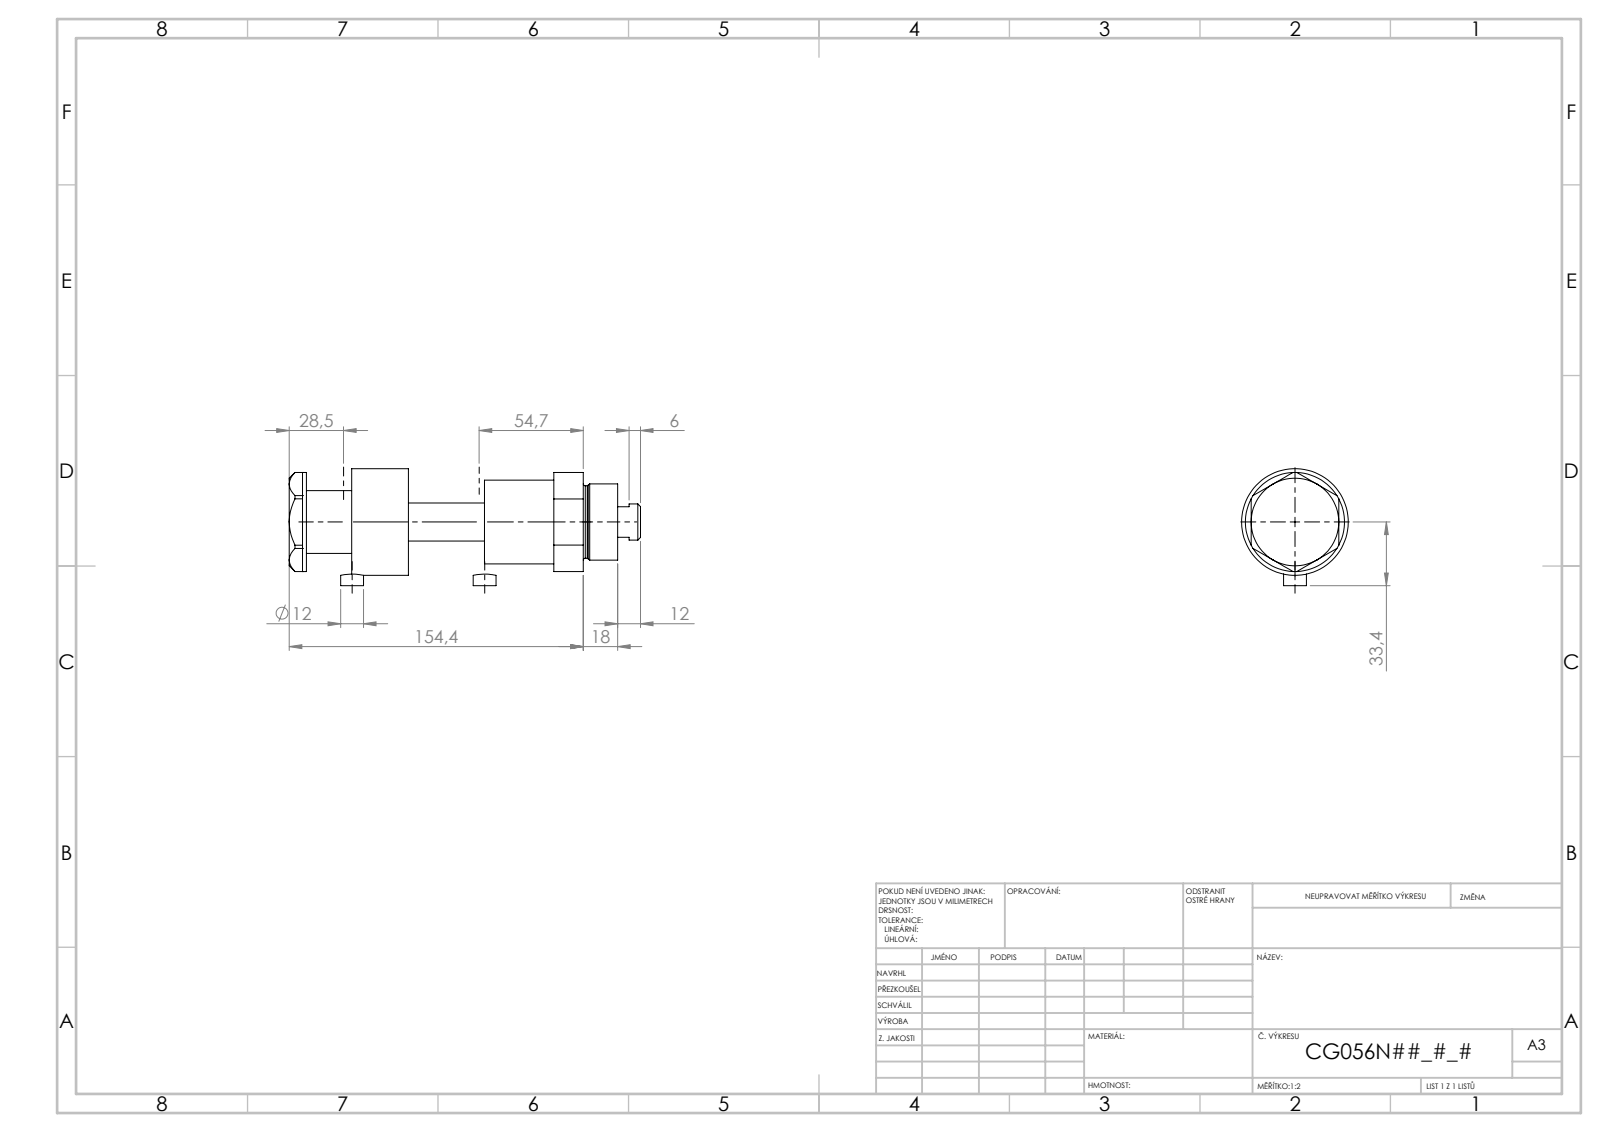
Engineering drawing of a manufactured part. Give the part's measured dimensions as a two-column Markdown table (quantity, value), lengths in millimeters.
| quantity | value |
| --- | --- |
| part name | V270CG_MIDDLE; V270CG_BACK; V270CG_VC; V270CG_FRONT |
| STEP written by | SolidWorks 2019 (CONFIG_CONTROL_DESIGN) |
| units | millimeters |
| bodies | 5 solids, 104 faces (51 planar, 33 cylindrical, 20 other) |
| overall size | 184.4 × 61.4 × 56 |
| volume | 235 738 mm³ |
| surface area | 44 743 mm² |
| round holes (diameter × count) | 6.5 × 1, 20 × 1, 21.5 × 1, 56 × 1 |
| round bosses / shafts (diameter × count) | 12 × 2, 52 × 1, 44 × 1, 40 × 1, 38 × 1, 33 × 1, 19 × 1 |
| main face-to-face distances | 29.75, 32.8, 62.55, 9, 23.8, 53.55, 102.5, 93.5, 69.7, 39.95 |
